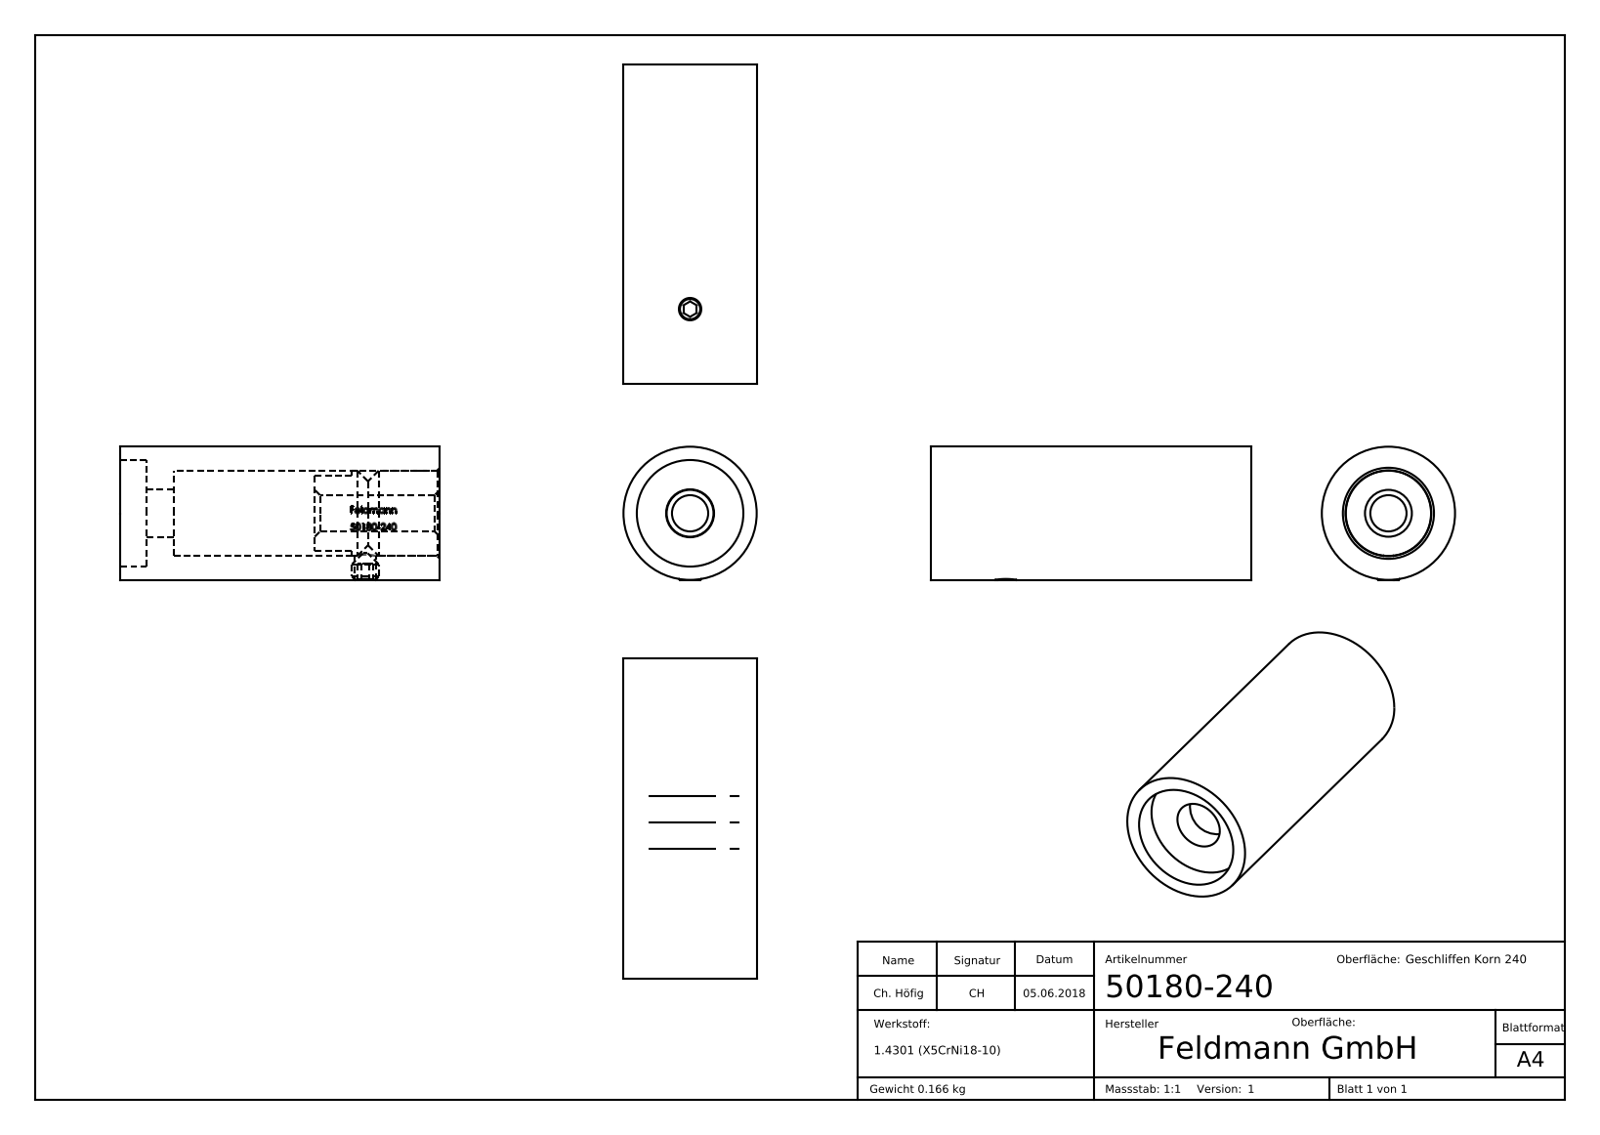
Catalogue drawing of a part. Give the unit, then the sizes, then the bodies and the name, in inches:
Units: inches
Overall size (bounding box): 2.362 × 0.984 × 0.984
Round holes (diameter × count): ⌀0.165 ×1, ⌀0.268 ×1, ⌀0.354 ×1, ⌀0.634 ×1, ⌀0.787 ×1
Round bosses / shafts (diameter × count): ⌀0.984 ×1, ⌀0.63 ×1, ⌀0.197 ×1
Partial cylindrical surfaces — rounded edges, fillets, slot ends (radius × count): R0.321 ×1
Main face-to-face distances: 0.197, 2.165, 2.362, 1.969, 0.394, 0.925, 1.043, 1.24, 1.437, 0.551
Volume: 1.279 in³ · Surface area: 16.62 in²
Bodies: 3 solids, 278 faces (108 planar, 50 cylindrical, 120 other)
Part name (STEP PRODUCT): DIN914_DIN 914 M5x5; 5x180-240-xx Konfig Teil2_5x180-240-xx Teil2; 50180-240; 5x180-240-xx Konfig Teil1_50180-240 Teil1
STEP written by: SolidWorks 2015 (CONFIG_CONTROL_DESIGN)
